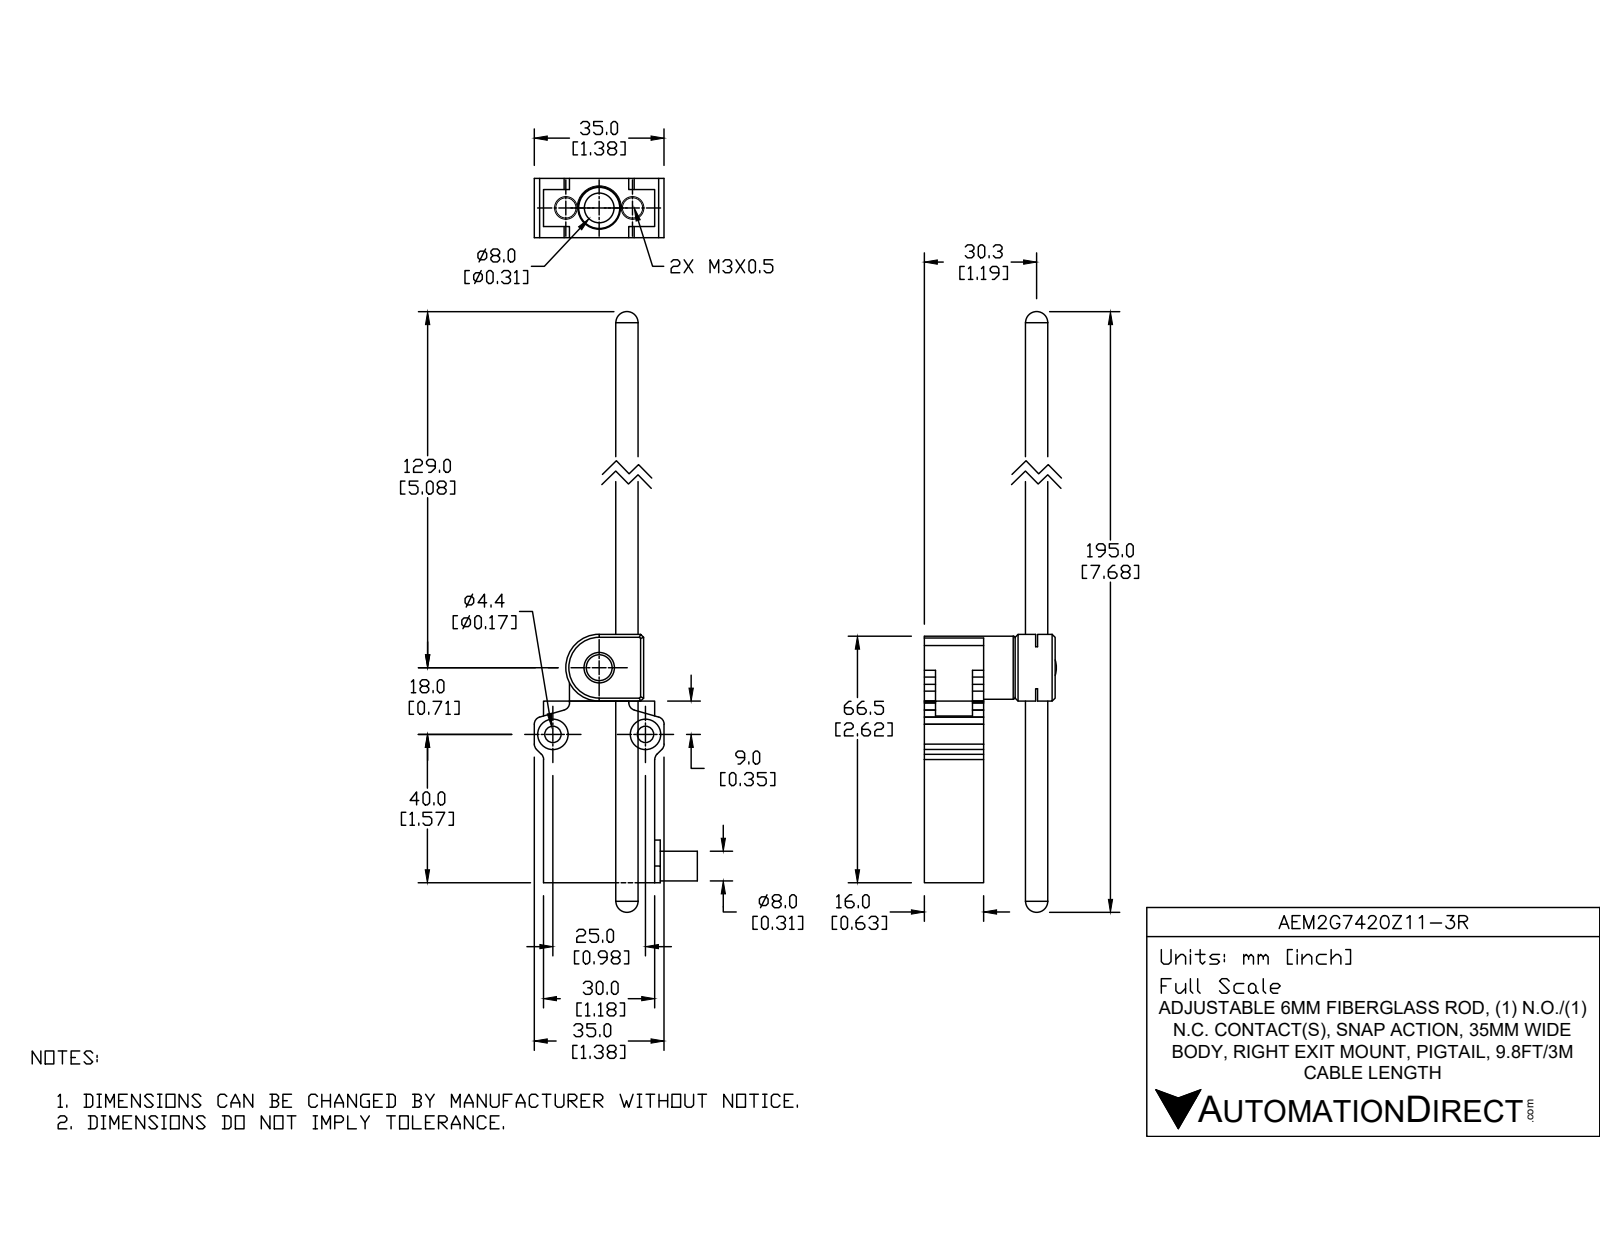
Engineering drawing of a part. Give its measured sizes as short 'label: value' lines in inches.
name: AEM2G7420Z11-3R
written by: SolidWorks 2017 (AUTOMOTIVE_DESIGN)
unit: in
bodies: 7 solids, 169 faces (95 planar, 57 cylindrical, 17 other)
size: 7.746 × 1.87 × 1.374
volume: 2.217 in³; area: 23.55 in²
holes: 2× ⌀0.118, 2× ⌀0.173, 2× ⌀0.323, 1× ⌀0.138, 1× ⌀0.197, 1× ⌀0.236, 1× ⌀0.315
bosses: 1× ⌀0.622, 1× ⌀0.323, 1× ⌀0.276
rounds: 8× R0.079, 1× R0.256, 1× R0.354
face distances: 0.63, 1.181, 0.177, 1.929, 0.354, 0.535, 1.165, 0.358, 0.28, 0.902
hole spacings: 0.863, 0.748, 0.857, 0.984, 1.065
